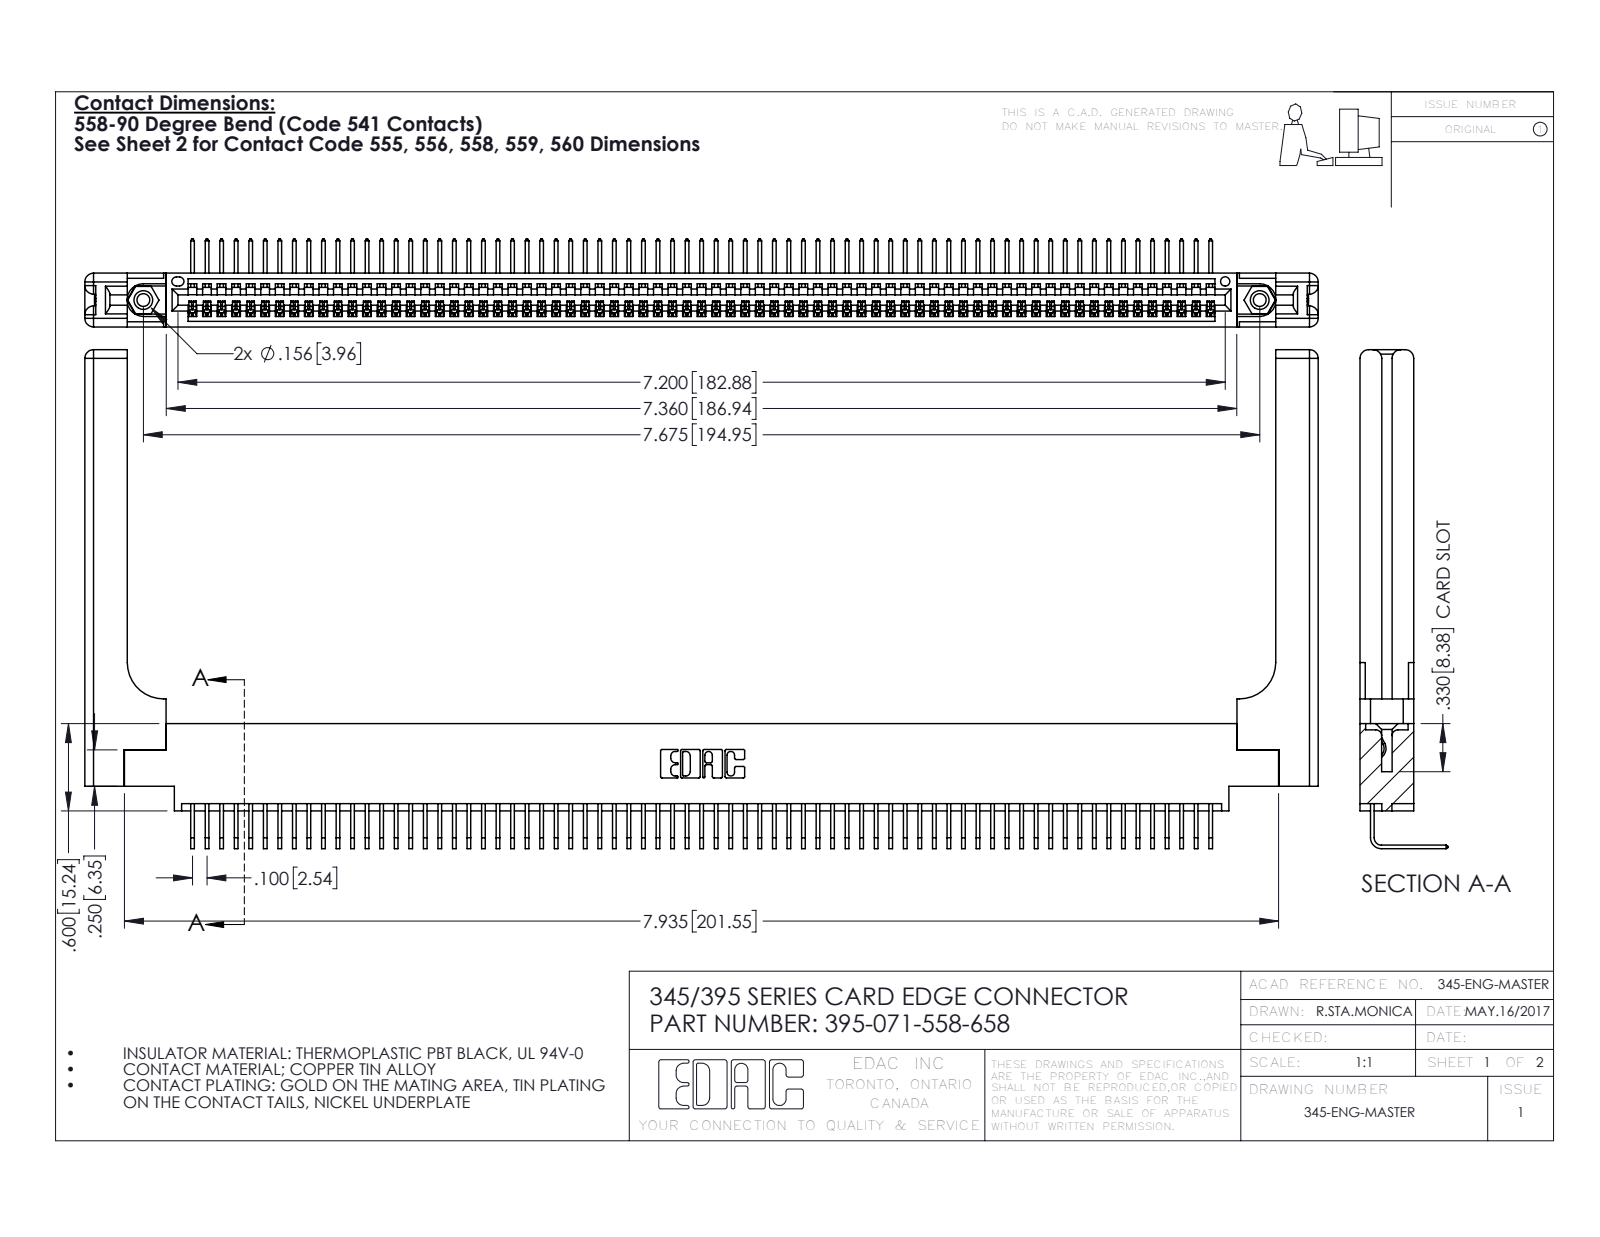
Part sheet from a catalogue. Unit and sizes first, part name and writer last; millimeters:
Units: millimetres
Overall size (bounding box): 215.4 × 87.1 × 15.4
Round holes (diameter × count): ⌀2.3 ×2, ⌀3.2 ×2, ⌀4 ×2, ⌀1.6 ×1
Round bosses / shafts (diameter × count): ⌀3.9 ×2
Partial cylindrical surfaces — rounded edges, fillets, slot ends (radius × count): R0.2 ×142, R0.3 ×22, R1.5 ×16, R0.2 ×6, R0.8 ×6, R0.7 ×3, R0.8 ×2, R0.8 ×2
Main face-to-face distances: 1.8, 9.4, 7.6, 2.5, 6.9, 0.6, 5.1, 5.7, 3.8, 3.8
Hole centre spacings: 6.9, 189, 194.9
Volume: 29 320 mm³ · Surface area: 34 880 mm²
Bodies: 76 solids, 4646 faces (3214 planar, 1372 cylindrical, 60 other)
Part name (STEP PRODUCT): 345-250-001_345-250-001-102; 395-071-558-658; 345-220-058_345-220-058; 345-292-001_558 Tail - 2 (+1 more)
STEP written by: SolidWorks 2016 (CONFIG_CONTROL_DESIGN)
